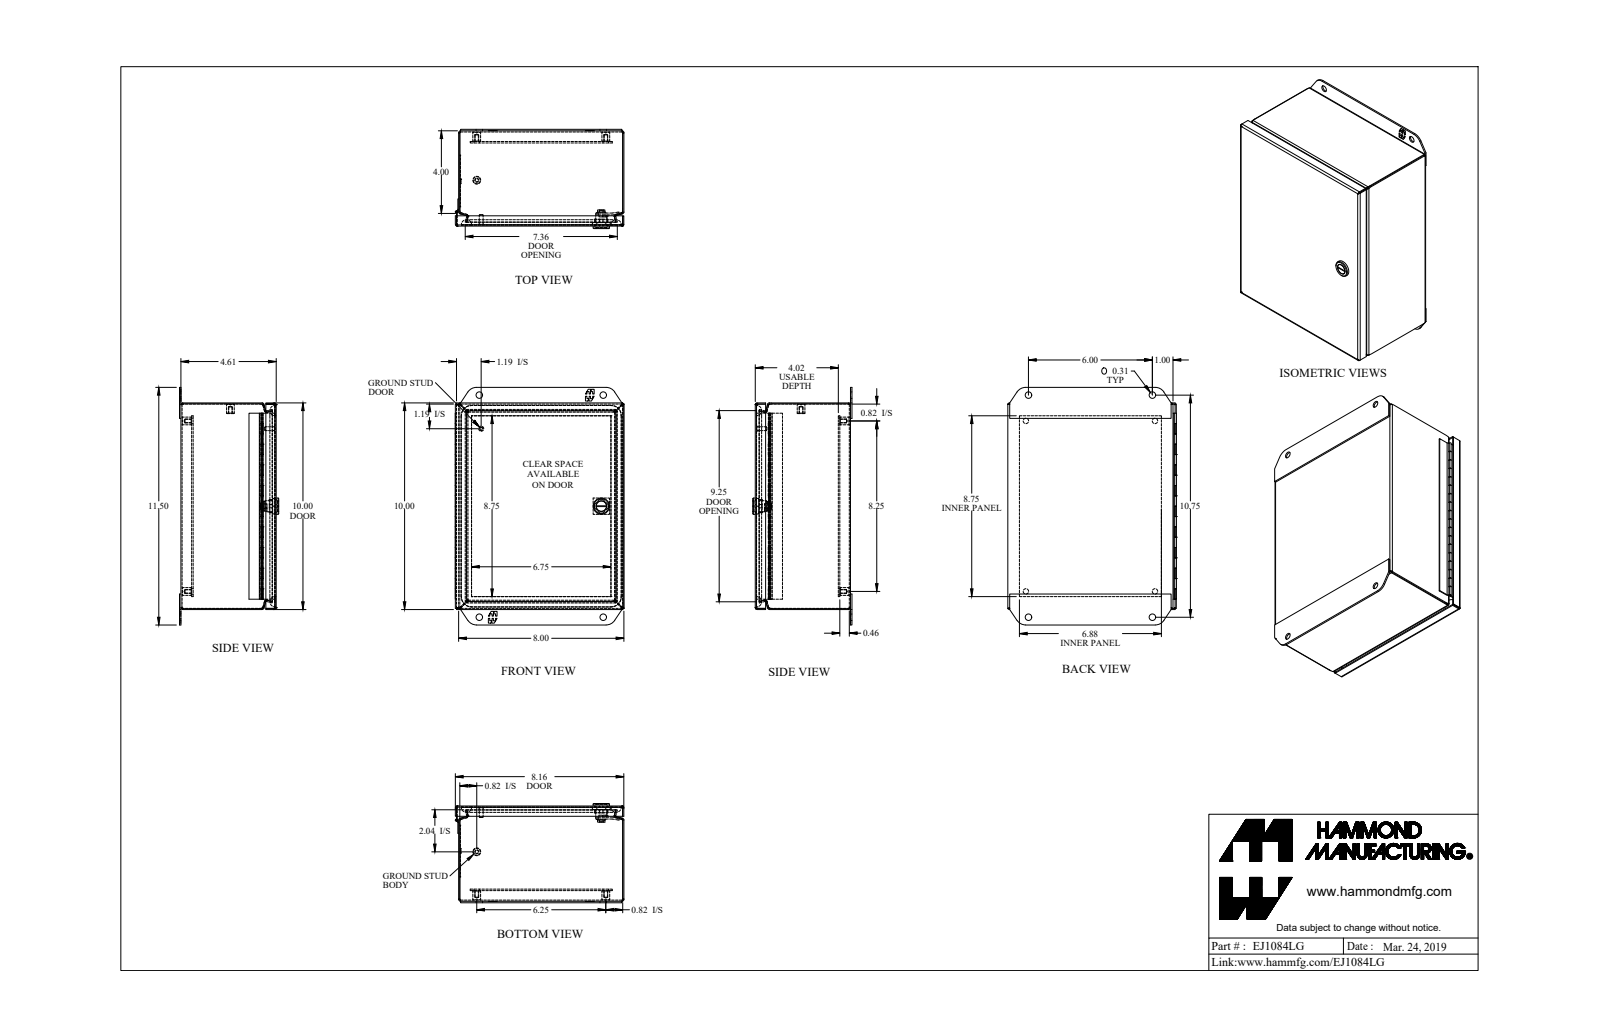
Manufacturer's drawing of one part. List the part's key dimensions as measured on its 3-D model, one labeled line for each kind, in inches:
Part name (STEP PRODUCT): EJ1084LG_Default
STEP written by: SolidWorks 2019 (CONFIG_CONTROL_DESIGN)
Units: inches
Bodies: 16 solids, 675 faces (377 planar, 206 cylindrical, 92 other)
Overall size (bounding box): 11.5 × 8.165 × 4.805
Volume: 29.4 in³ · Surface area: 966.9 in²
Round holes (diameter × count): ⌀0.156 ×5, ⌀0.265 ×4, ⌀0.313 ×4, ⌀0.05 ×1, ⌀0.516 ×1
Round bosses / shafts (diameter × count): ⌀0.375 ×5, ⌀0.788 ×1, ⌀0.535 ×1, ⌀0.496 ×1, ⌀0.435 ×1, ⌀0.25 ×1, ⌀0.188 ×1, ⌀0.1 ×1
Partial cylindrical surfaces — rounded edges, fillets, slot ends (radius × count): R0.029 ×16, R0.086 ×16, R0.281 ×10, R0.25 ×4, R0.499 ×4, R0.5 ×4, R0.06 ×2, R0.539 ×2
Main face-to-face distances: 0.057, 4.554, 0.072, 0.589, 4.611, 4.497, 7.943, 9.943, 0.46, 0.517
Hole centre spacings: 1.256, 1.257, 4.131, 6, 6.25, 6.251, 6.252, 7.307
